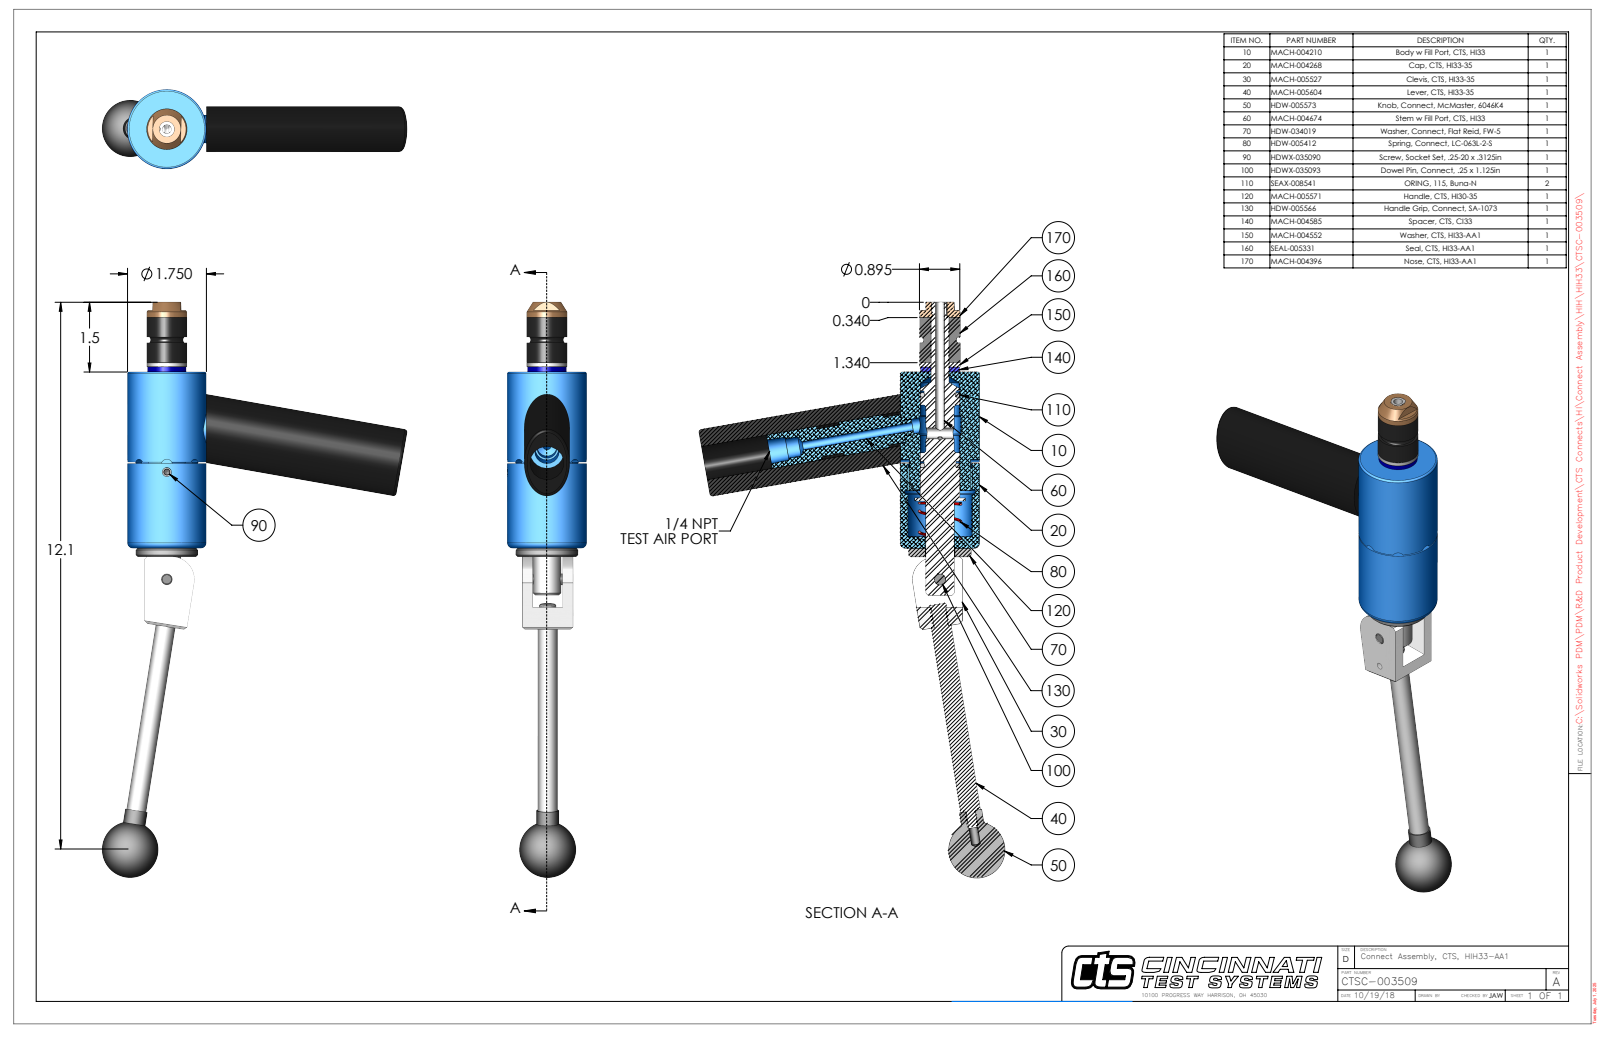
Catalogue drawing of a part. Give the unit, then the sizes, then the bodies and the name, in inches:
Units: inches
Overall size (bounding box): 12.751 × 6.763 × 1.75
Round holes (diameter × count): ⌀0.201 ×2, ⌀0.313 ×2, ⌀0.15 ×1, ⌀0.187 ×1, ⌀0.204 ×1, ⌀0.249 ×1, ⌀0.25 ×1, ⌀0.251 ×1, ⌀0.39 ×1, ⌀0.397 ×1, ⌀0.403 ×1, ⌀0.438 ×1
Round bosses / shafts (diameter × count): ⌀0.375 ×2, ⌀0.312 ×2, ⌀0.25 ×2, ⌀1.75 ×1, ⌀1.38 ×1, ⌀0.895 ×1, ⌀0.895 ×1, ⌀0.858 ×1
Partial cylindrical surfaces — rounded edges, fillets, slot ends (radius × count): R0.125 ×4, R0.029 ×2, R0.151 ×1, R0.33 ×1, R0.5 ×1, R0.695 ×1, R0.833 ×1
Main face-to-face distances: 3.907, 1.12, 4.095, 0.188, 0.888, 0.232, 0.232, 0.656, 0.888, 1.207
Hole centre spacings: 0.74, 2.376, 3.116
Volume: 17.65 in³ · Surface area: 110.8 in²
Bodies: 11 solids, 303 faces (109 planar, 125 cylindrical, 69 other)
Part name (STEP PRODUCT): CTSC-003509
STEP written by: SolidWorks 2023 (AUTOMOTIVE_DESIGN)
